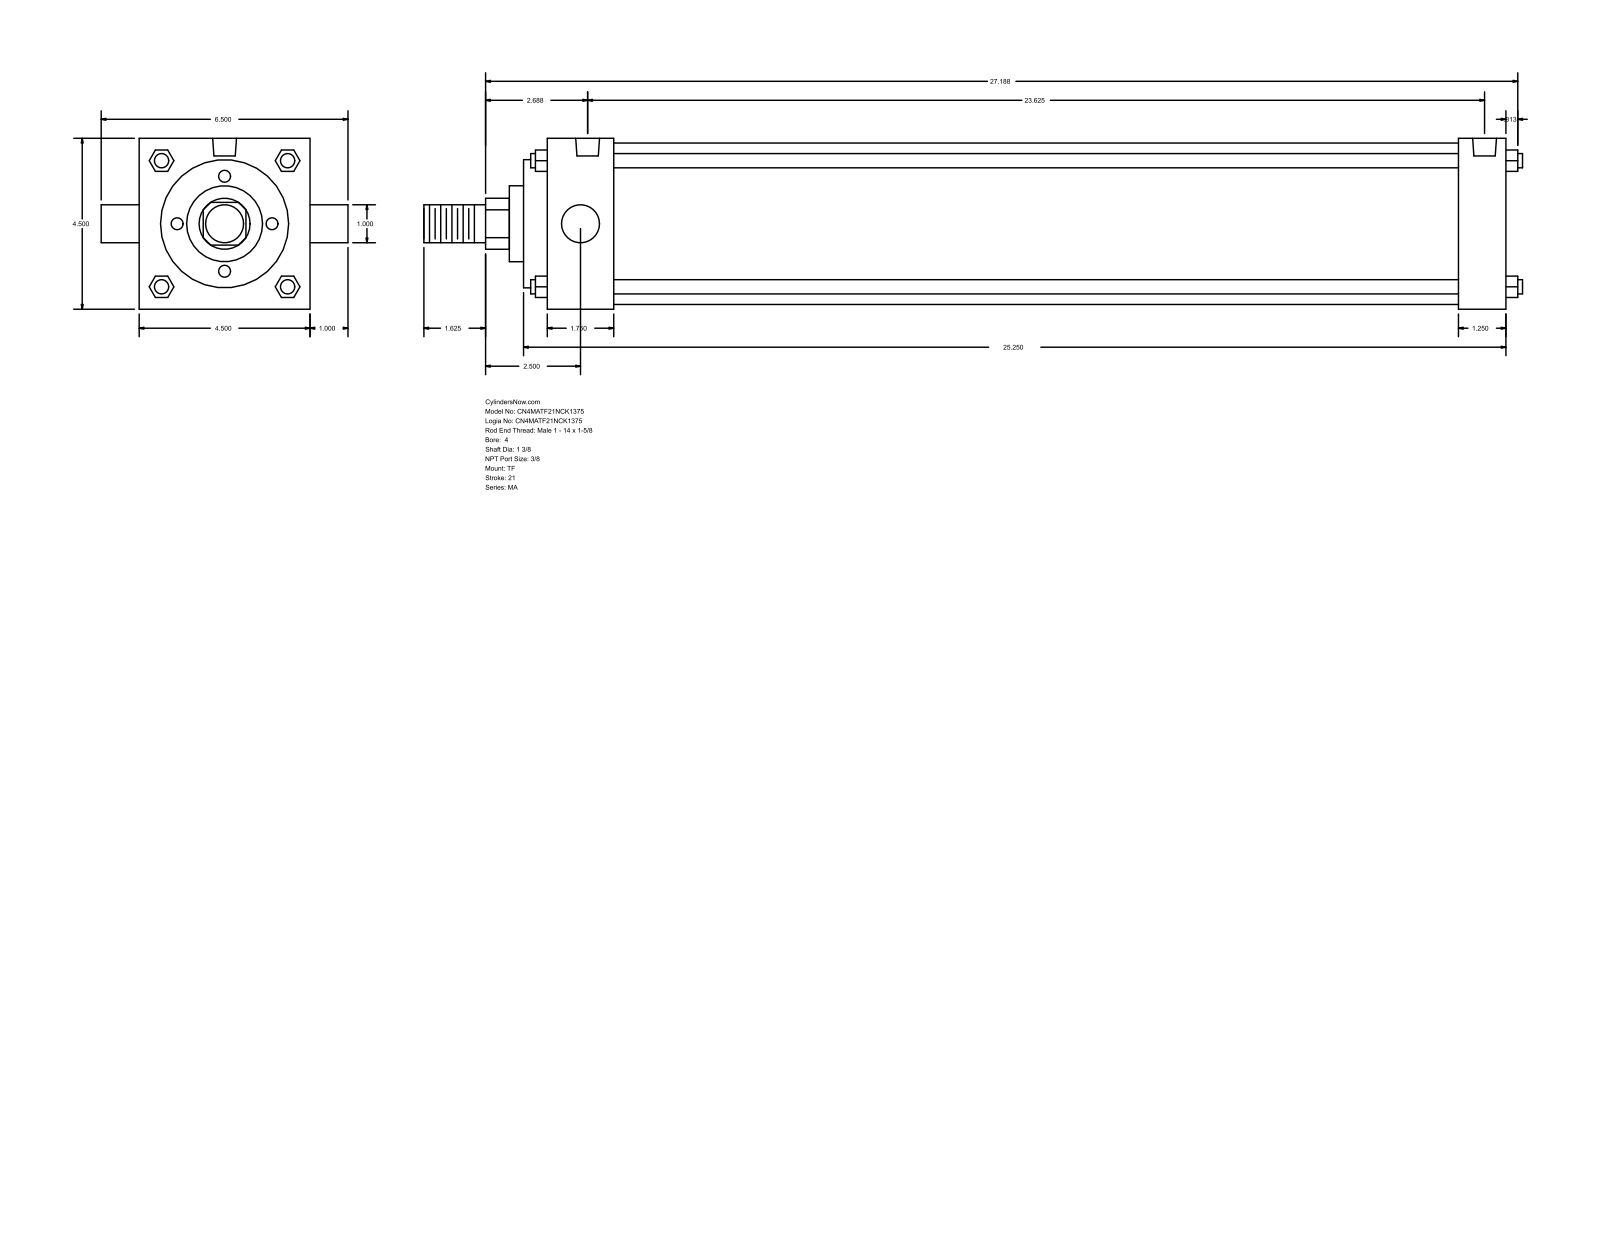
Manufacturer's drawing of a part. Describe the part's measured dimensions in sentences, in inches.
The part is named "MA_TF__0400_1.375". Its 3-D file was written by "GSSL Pune (CONFIG_CONTROL_DESIGN)". It is 0 solids with 122 faces: 93 planar, 29 cylindrical and 0 other. Overall it measures 28.937 by 6.5 by 4.5 inches. Round holes: 3 of diameter 0.437, 2 of diameter 0.627. Round bosses or shafts: 4 of diameter 0.375, 2 of diameter 1, 1 of diameter 4.25, 1 of diameter 3.375, 1 of diameter 2, 1 of diameter 1.375. Partial cylindrical surfaces (rounded edges, fillets, slot ends): 1 of radius 0.672. The main face-to-face distances are 4.5, 25.25, 25.875, 0.625, 24.625, 24, 1.25, 2.375, 1.75, 22.25. The hole center spacings are 0.187, 0.188, 23.25, 23.437, 23.438, 23.625.
